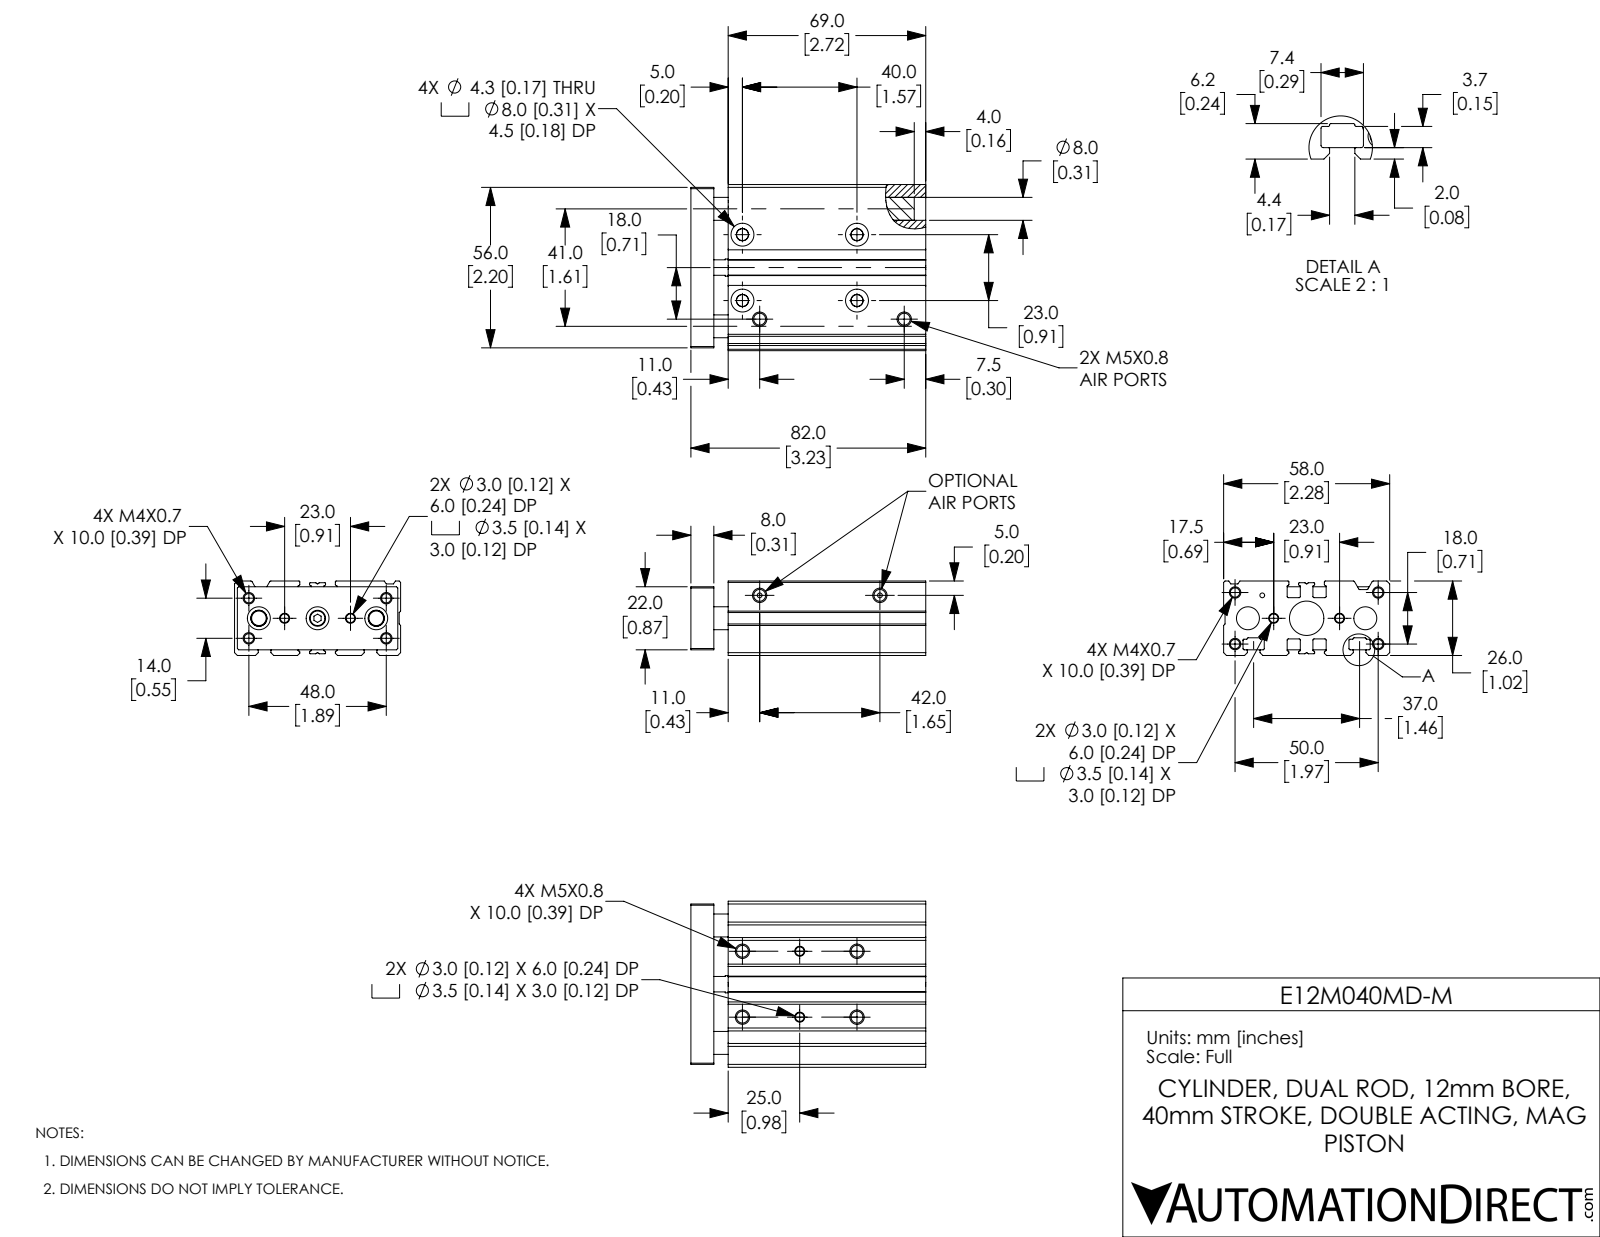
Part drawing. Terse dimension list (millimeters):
name: E12M040MD-D_BODY; E12M040MD-M_ENDPLATE; E12M040MD-M
written by: SolidWorks 2019 (CONFIG_CONTROL_DESIGN)
unit: mm
bodies: 5 solids, 413 faces (137 planar, 188 cylindrical, 88 other)
size: 82 × 58 × 26
volume: 92 462 mm³; area: 38 965 mm²
holes: 8× ⌀3.24, 8× ⌀4.13, 7× ⌀8, 4× ⌀3, 4× ⌀3.5, 4× ⌀4.3, 3× ⌀1.67, 3× ⌀4, 2× ⌀5.59, 1× ⌀8, 1× ⌀12, 1× ⌀12
bosses: 1× ⌀6, 1× ⌀5.59
rounds: 20× R0.4, 18× R0.2, 8× R0.25, 6× R0.3, 4× R0.5
face distances: 26, 8, 5.8, 58, 2, 13, 9, 24, 74, 5
hole spacings: 2.24, 7.83, 10.06, 14.33, 16.03, 16.22, 20, 23
